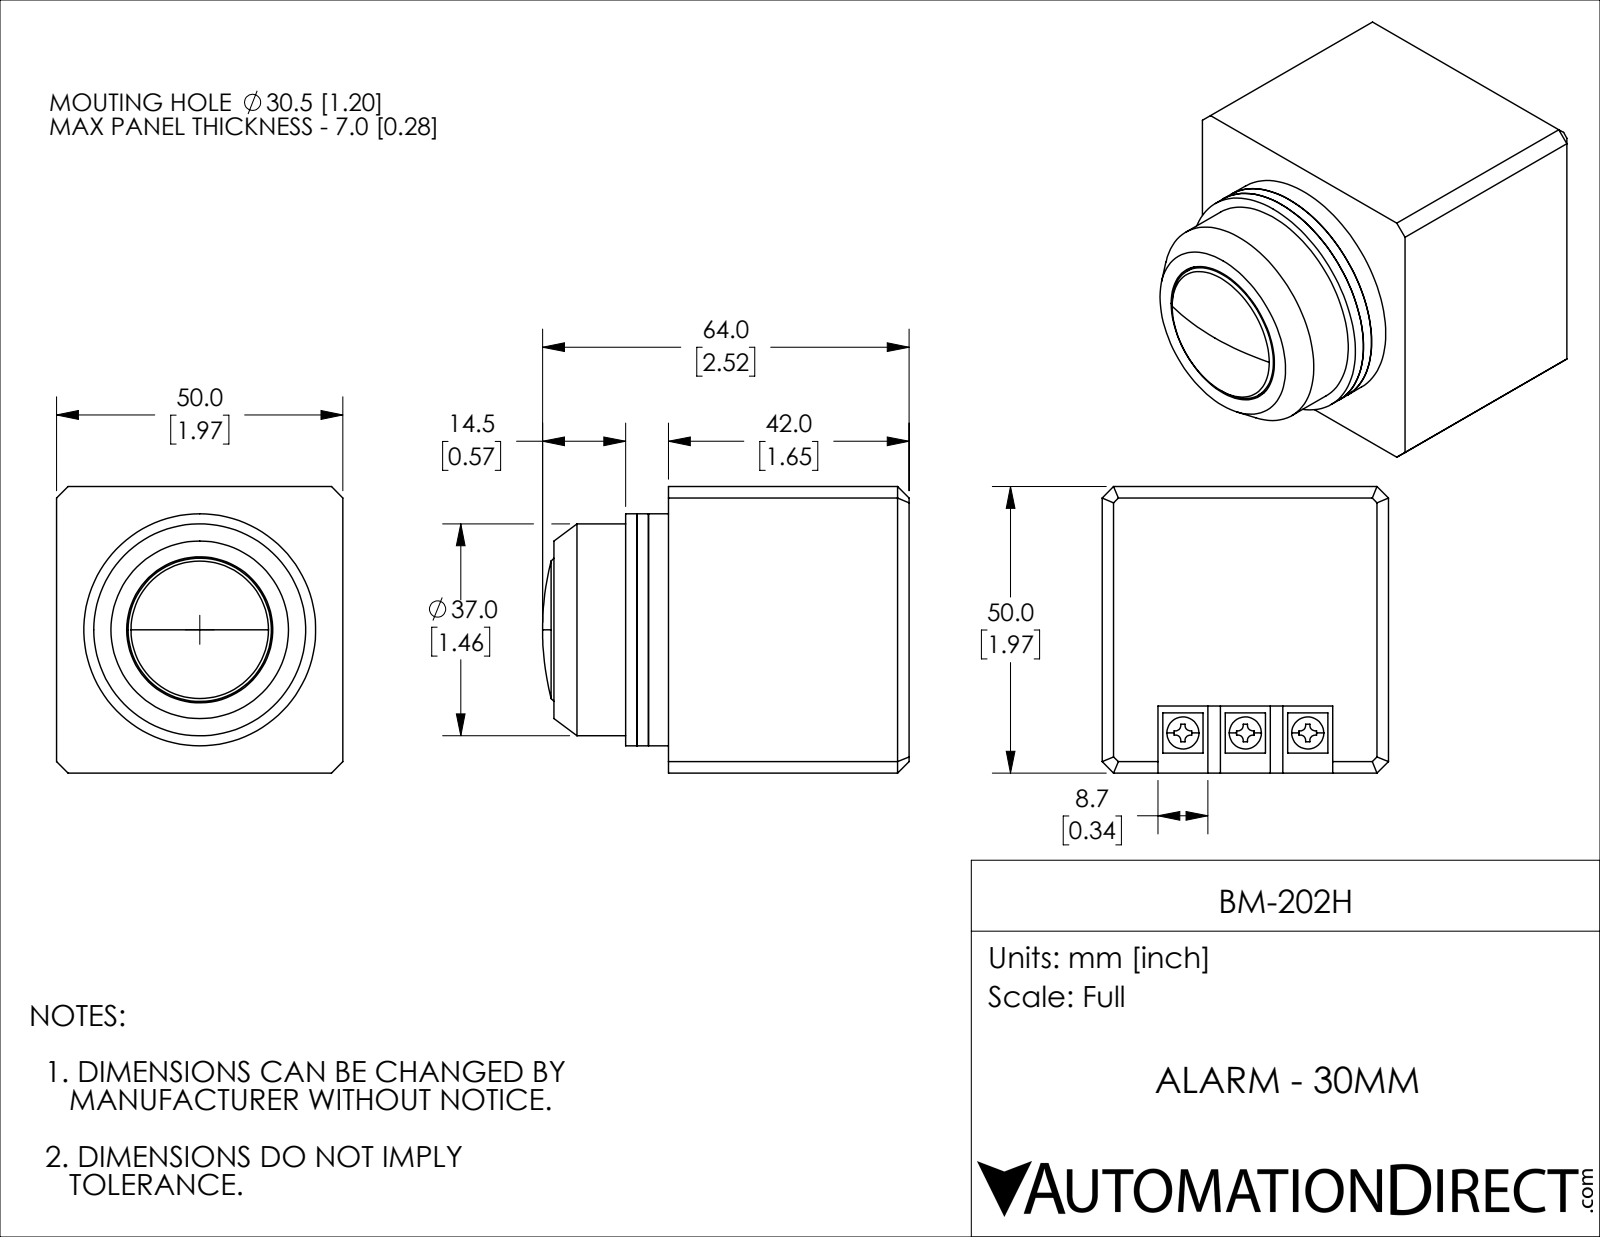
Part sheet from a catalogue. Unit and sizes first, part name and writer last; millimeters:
Units: millimetres
Overall size (bounding box): 64 × 50 × 50
Round holes (diameter × count): ⌀25.5 ×1, ⌀30 ×1, ⌀30.5 ×1
Round bosses / shafts (diameter × count): ⌀40.5 ×1, ⌀37 ×1, ⌀25 ×1
Main face-to-face distances: 50, 2, 42, 45.5, 4, 3.5, 5.5, 47.5, 7.5, 49.5
Volume: 122 600 mm³ · Surface area: 24 340 mm²
Bodies: 5 solids, 120 faces (68 planar, 22 cylindrical, 30 other)
Part name (STEP PRODUCT): BM-202H
STEP written by: SolidWorks 2018 (AUTOMOTIVE_DESIGN)
